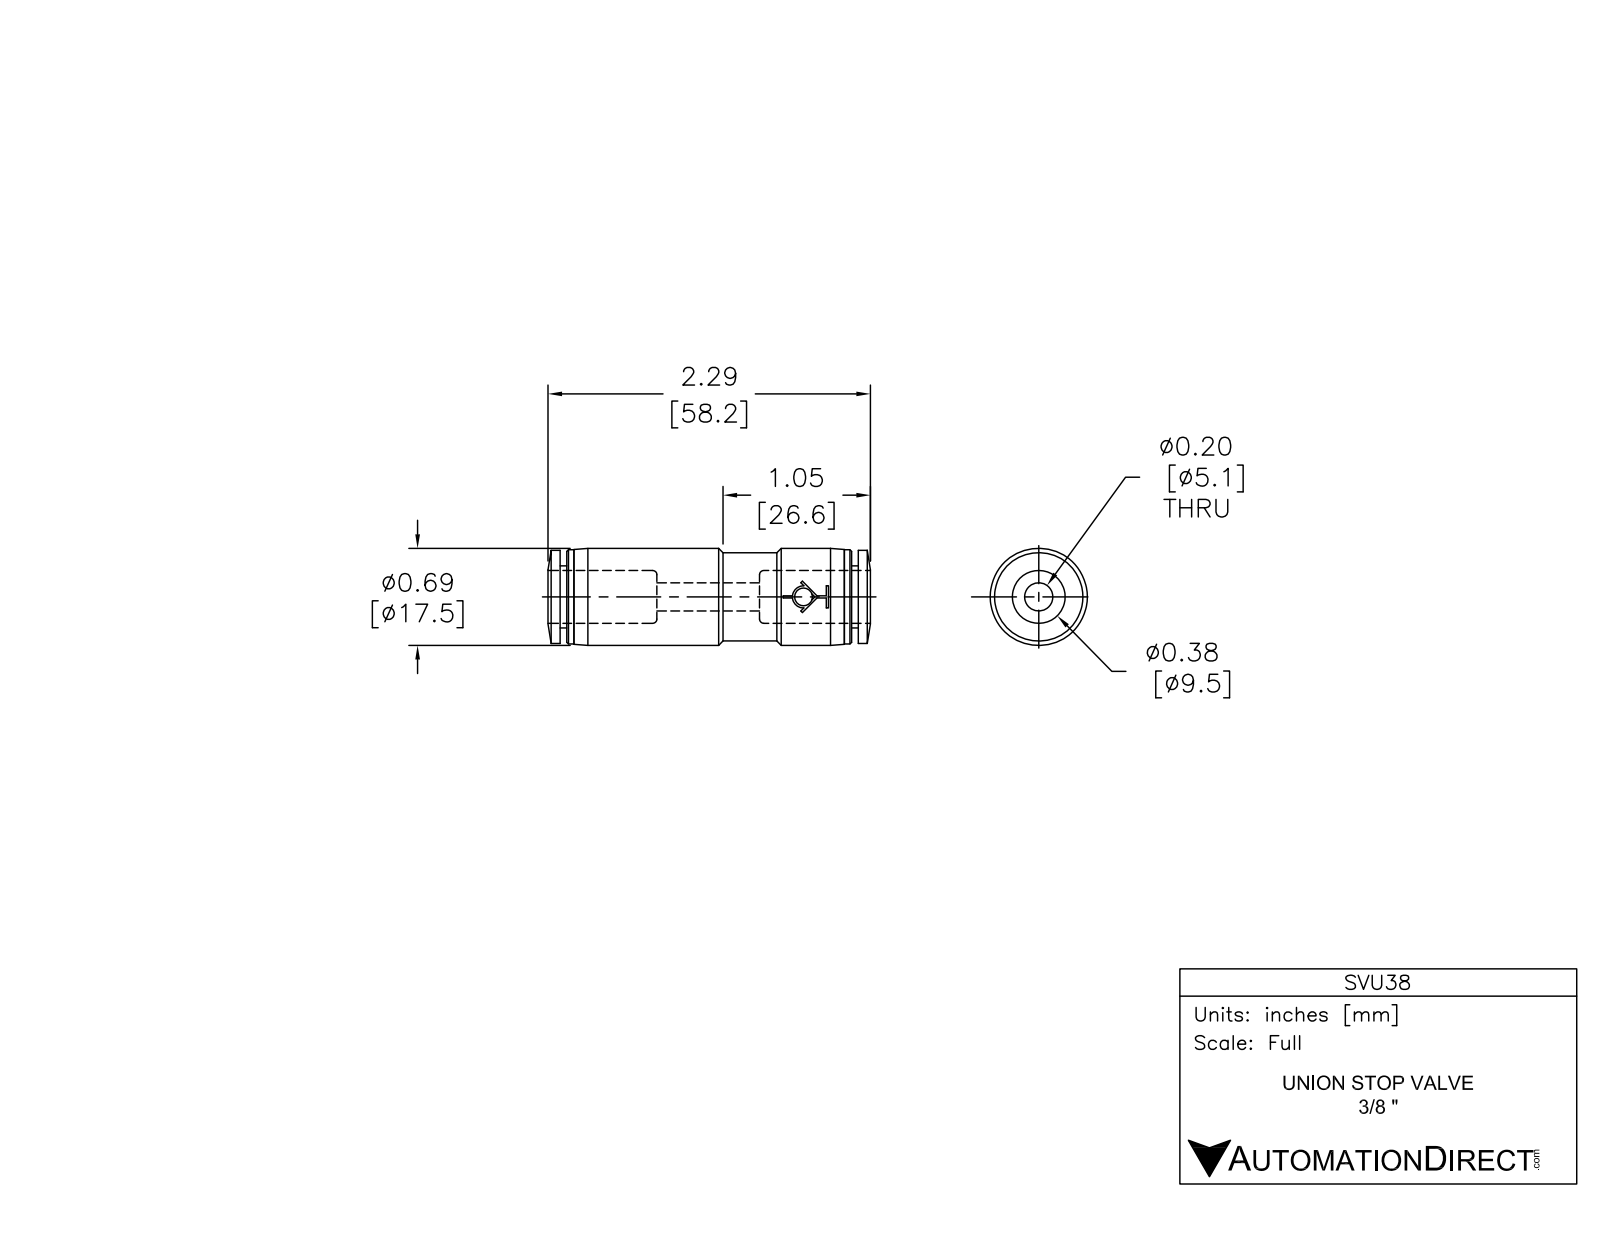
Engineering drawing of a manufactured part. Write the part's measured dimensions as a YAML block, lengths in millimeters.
part_name: "SVU38"
step_written_by: "SolidWorks 2015 (AUTOMOTIVE_DESIGN)"
units: millimeters
bodies: {solids: 1, faces: 82, planar: 24, cylindrical: 30, other: 28}
overall_size: [58.2, 17.6, 17.5]
volume: 8930
surface_area: 5587
round_holes:
  - {diameter: 3.2, count: 1}
  - {diameter: 8.5, count: 1}
  - {diameter: 9.8, count: 1}
round_bosses_or_shafts:
  - {diameter: 17.5, count: 1}
  - {diameter: 17, count: 1}
  - {diameter: 16.8, count: 1}
  - {diameter: 15.9, count: 1}
  - {diameter: 11.2, count: 1}
partial_cylinders:
  - {radius: 2, count: 1}
  - {radius: 8.8, count: 1}
face_to_face_distances: [1.2, 52.6, 53.8, 51.4, 17.9, 35.9, 16.7, 34.7, 18, 2.5]
